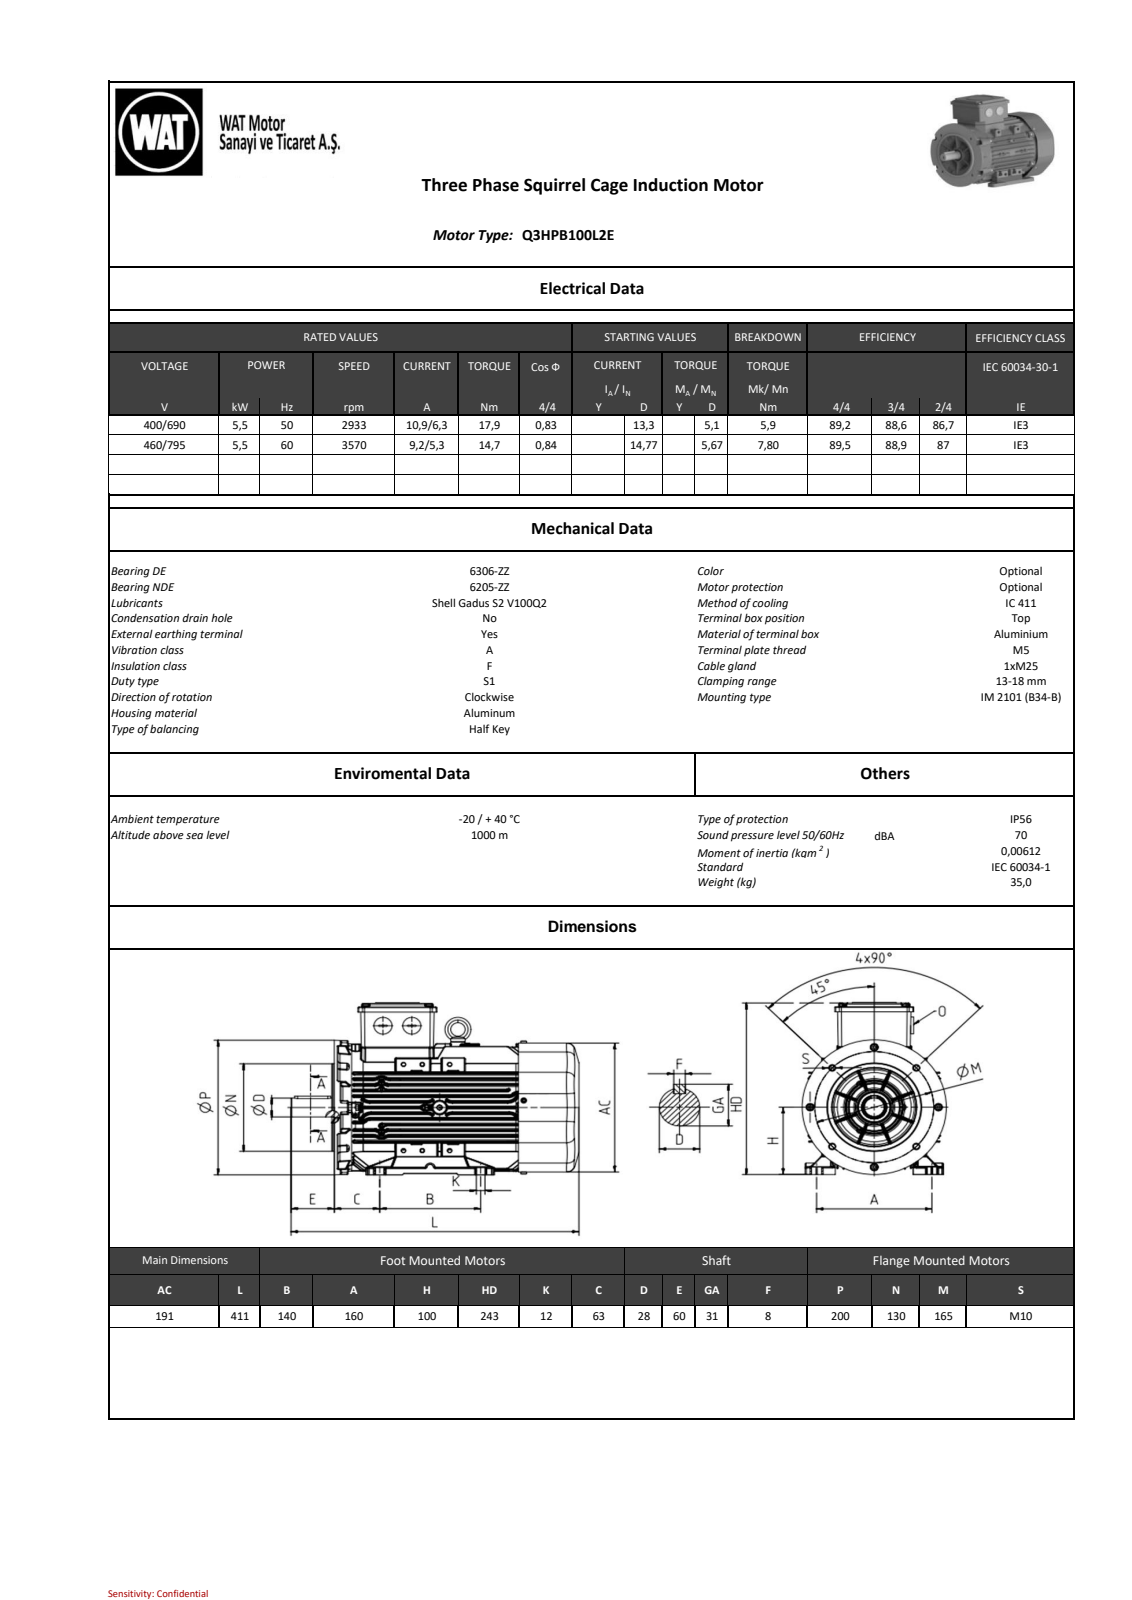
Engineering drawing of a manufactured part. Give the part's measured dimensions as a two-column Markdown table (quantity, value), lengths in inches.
| quantity | value |
| --- | --- |
| part name | QH100 B35 KTA-M2_stp_objects |
| STEP written by | SIEMENS PLM Software NX2206.8101 (AUTOMOTIVE_DESIGN) |
| units | inches |
| bodies | 0 solids, 5843 faces (1291 planar, 2211 cylindrical, 2341 other) |
| overall size | 16.191 × 9.55 × 7.874 |
| round holes (diameter × count) | 0.256 × 4, 0.335 × 4, 0.453 × 4, 0.394 × 1, 0.413 × 1, 0.472 × 1, 1.728 × 1, 1.736 × 1, 2.047 × 1, 2.26 × 1, 3.071 × 1, 3.504 × 1 |
| round bosses / shafts (diameter × count) | 0.315 × 8, 0.472 × 4, 5.118 × 1, 4.469 × 1, 3.681 × 1, 2.402 × 1, 1.181 × 1, 1.142 × 1 |
| partial cylindrical surfaces (radius × count) | 0.031 × 561, 0.039 × 534, 0.079 × 118, 0.059 × 81, 0.02 × 52, 0.032 × 52, 0.197 × 36, 0.591 × 26 |
| main face-to-face distances | 0.336, 0.333, 0.333, 3.002, 0.666, 3.679, 1.007, 0.671, 3.019, 2.348 |
| hole center spacings | 2.595, 6.239, 3.248, 3.504, 4.594, 4.956, 2.52, 2.636 |
